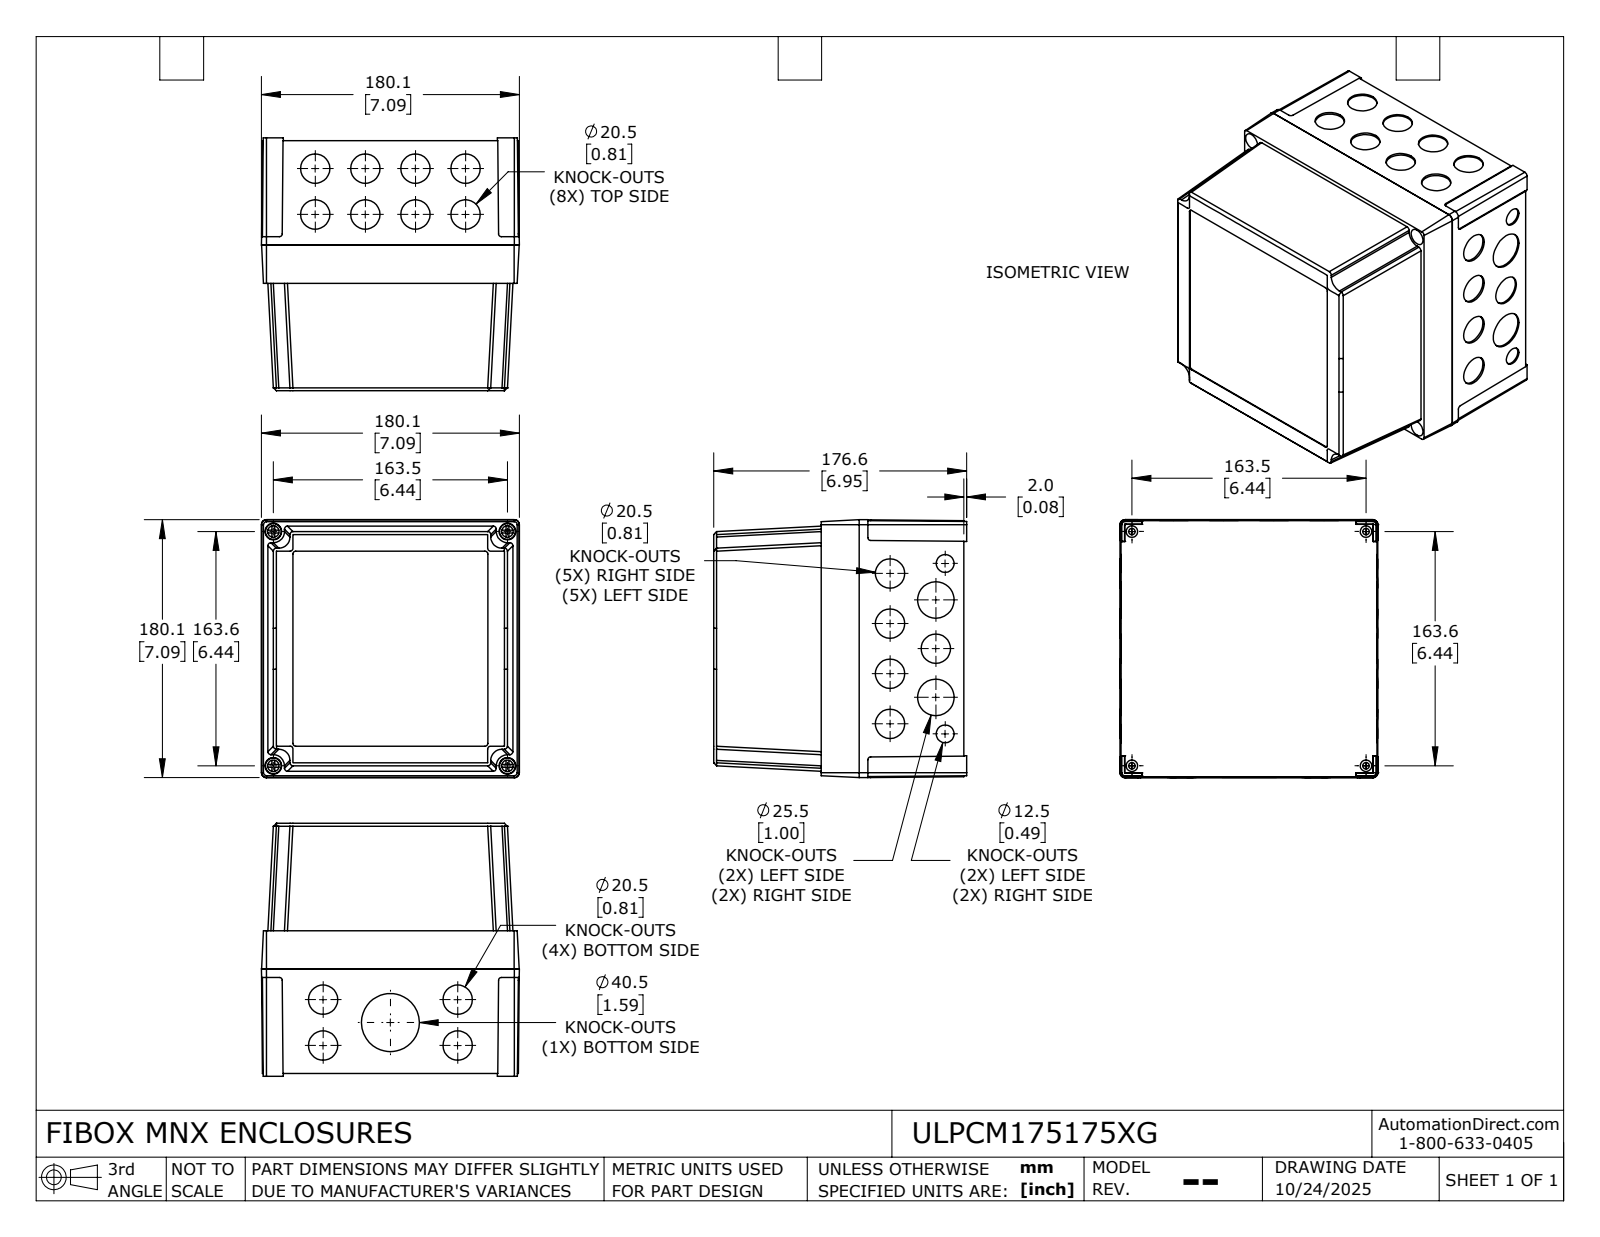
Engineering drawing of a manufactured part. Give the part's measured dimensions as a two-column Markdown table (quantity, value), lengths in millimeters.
| quantity | value |
| --- | --- |
| part name | ULPCM175175XT_Default |
| STEP written by | SolidWorks 2024 (CONFIG_CONTROL_DESIGN) |
| units | millimeters |
| bodies | 12 solids, 566 faces (370 planar, 148 cylindrical, 48 other) |
| overall size | 180.1 × 180.1 × 176.6 |
| volume | 525 356 mm³ |
| surface area | 377 624 mm² |
| round holes (diameter × count) | 20.5 × 17, 3.2 × 12, 4 × 12, 8 × 8, 4.5 × 4, 11.6 × 4, 12.5 × 2, 25.5 × 2, 40.5 × 1 |
| round bosses / shafts (diameter × count) | 8 × 12, 2.5 × 8, 11 × 4, 7.2 × 4 |
| partial cylindrical surfaces (radius × count) | 2 × 8, 2.1 × 8, 5 × 4, 7.8 × 4 |
| main face-to-face distances | 1.5, 3, 4.2, 171.6, 168.6, 2.5, 174.1, 171.1, 4.56, 3.06 |
| hole center spacings | 163.5, 35, 33.85, 50, 72.8, 82.59, 121.66, 132.27 |
